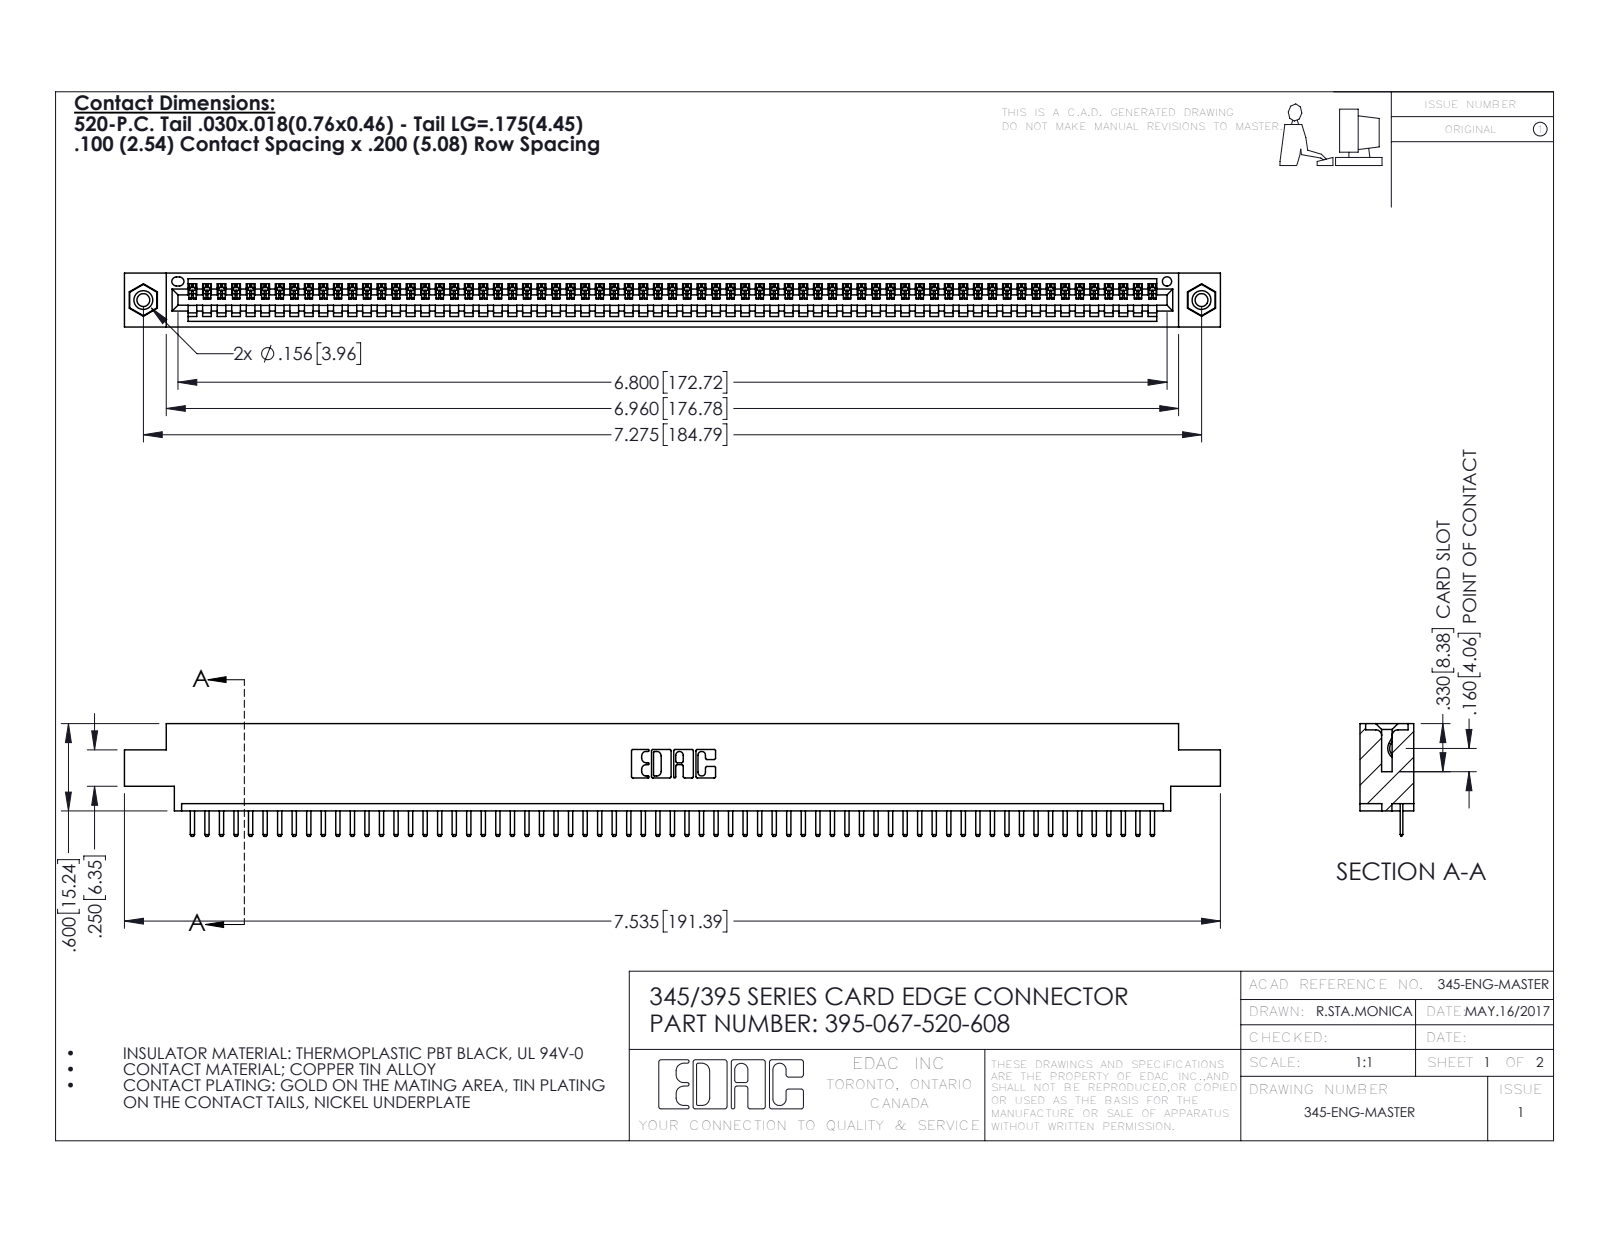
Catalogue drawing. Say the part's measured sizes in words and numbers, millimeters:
The part is named "345 Part_0.170 Offset - 0.156 Dia-TI; 345-292-001_345-293-120; 395-067-520-608; 345-250-001_345-250-003-102". Its 3-D file was written by "SolidWorks 2016 (CONFIG_CONTROL_DESIGN)". It is 70 solids with 4344 faces: 2930 planar, 1398 cylindrical and 16 other. Overall it measures 191.4 by 19.7 by 9.4 millimeters. Its volume is 18 070 cubic millimeters and its surface area 23 870 square millimeters. Round holes: 2 of diameter 2.3, 2 of diameter 3.2, 2 of diameter 4, 1 of diameter 1.6. Round bosses or shafts: 2 of diameter 3.9. Partial cylindrical surfaces (rounded edges, fillets, slot ends): 136 of radius 0.3, 134 of radius 0.2, 22 of radius 0.3, 6 of radius 0.2, 6 of radius 0.8, 3 of radius 0.7, 2 of radius 0.8, 2 of radius 1. The main face-to-face distances are 1.8, 7.6, 9.4, 5.1, 2.5, 6.9, 0.6, 5.7, 1.8, 4.4. The hole center spacings are 6.9, 178.8, 184.8.
